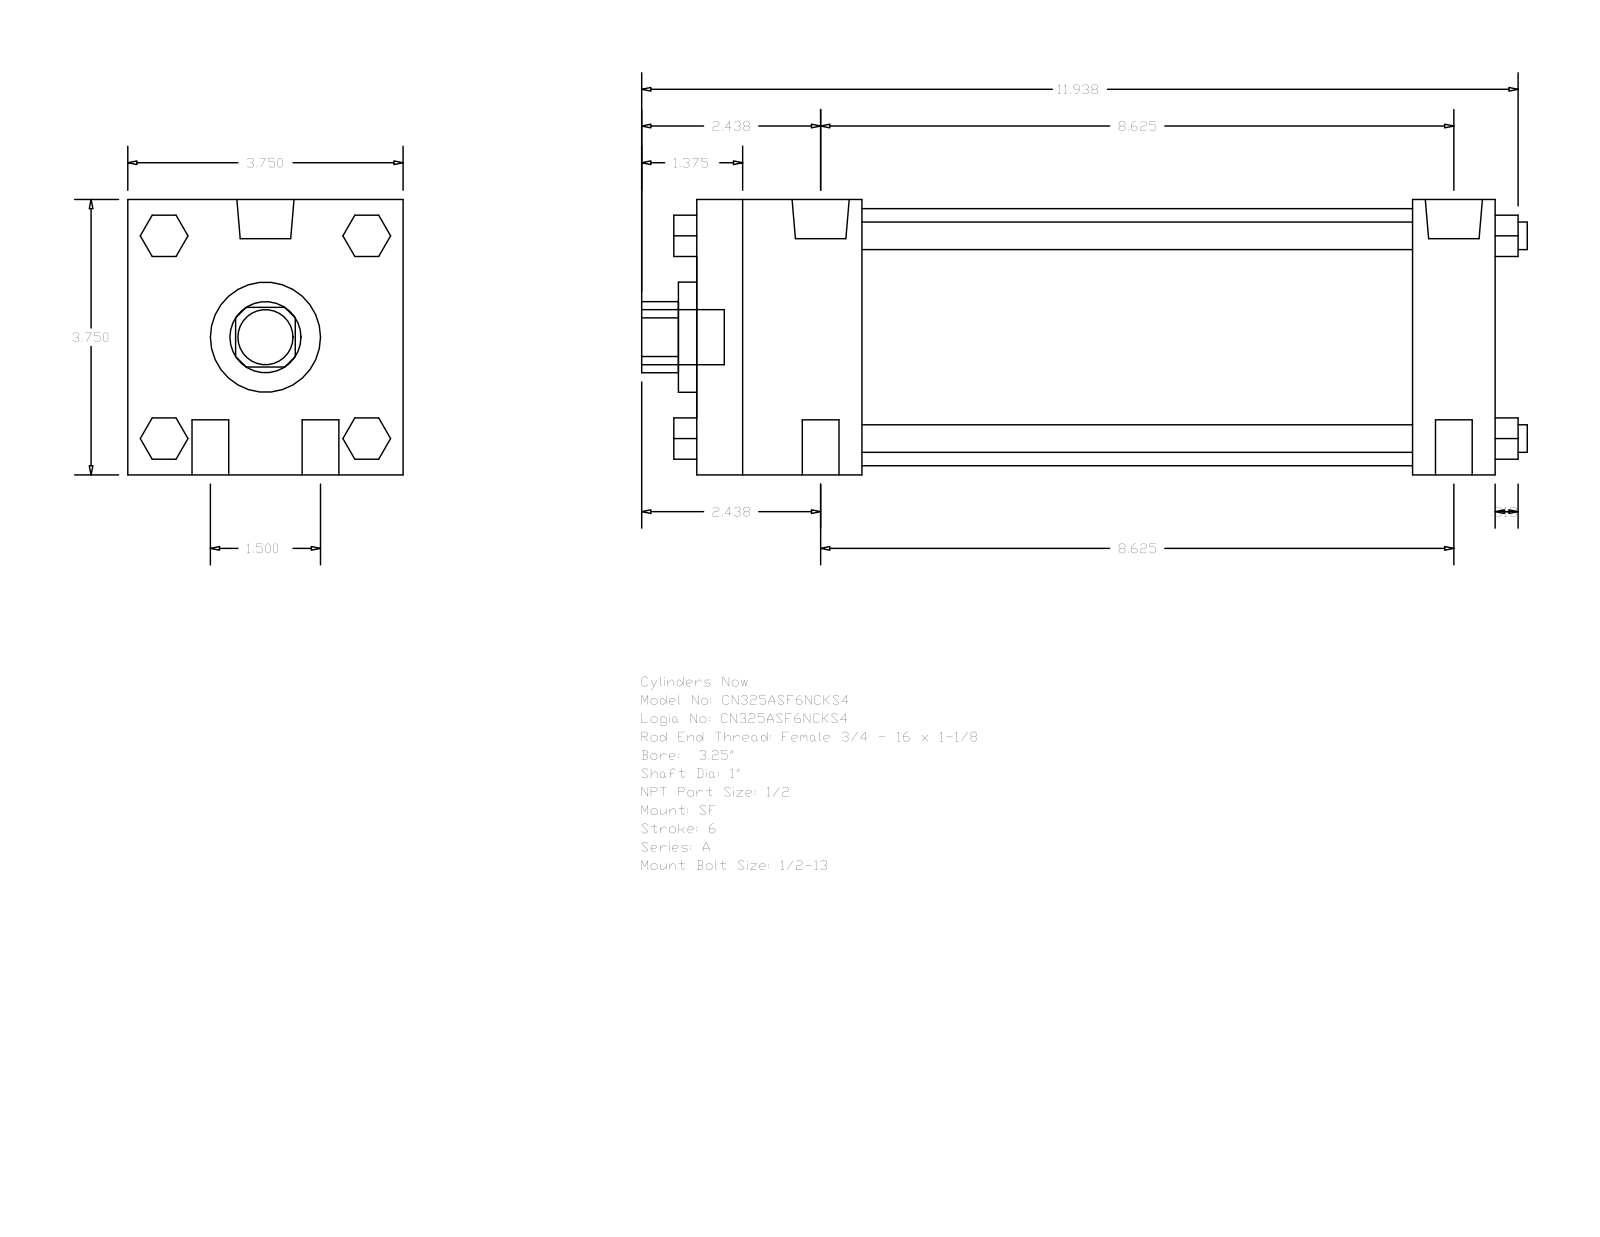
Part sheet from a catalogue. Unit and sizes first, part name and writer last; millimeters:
Units: millimetres
Overall size (bounding box): 306.39 × 95.25 × 95.25
Round holes (diameter × count): ⌀25.4 ×1, ⌀38.1 ×1, ⌀88.9 ×1
Round bosses / shafts (diameter × count): ⌀12.7 ×4, ⌀9.53 ×4, ⌀19.77 ×2, ⌀8.73 ×2, ⌀19.05 ×1
Partial cylindrical surfaces — rounded edges, fillets, slot ends (radius × count): R12.29 ×1
Main face-to-face distances: 95.24, 276.22, 28.57, 247.65, 57.15, 190.5, 219.07, 14.28, 35.05, 60.71
Bodies: 0 solids, 124 faces (94 planar, 30 cylindrical, 0 other)
Part name (STEP PRODUCT): A_SF__0325_1
STEP written by: GSSL Pune (CONFIG_CONTROL_DESIGN)
